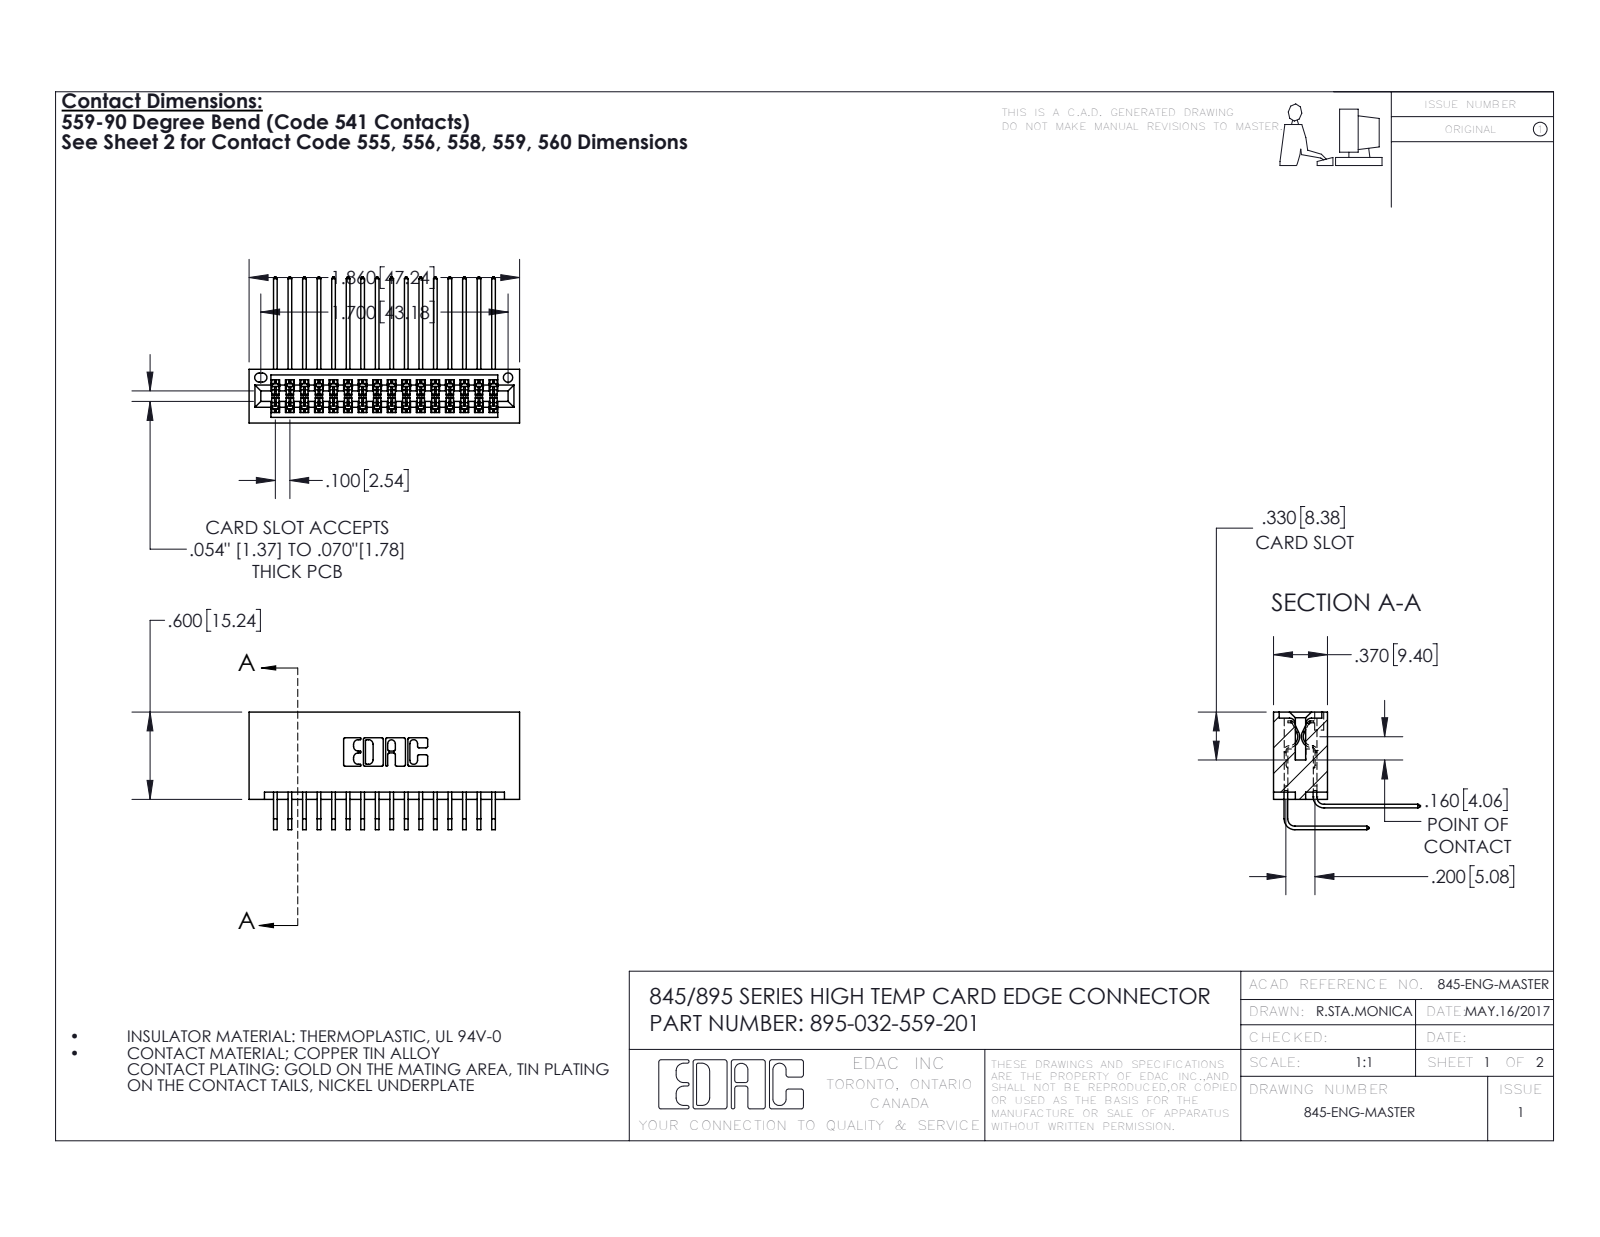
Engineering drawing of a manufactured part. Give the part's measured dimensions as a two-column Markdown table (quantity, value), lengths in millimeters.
| quantity | value |
| --- | --- |
| part name | 395-032-559-201; 345 Part_No Mounting Lugs; 345-292-001_559 Tail - 2; 345-292-001_558 559 Tail - 1 |
| STEP written by | SolidWorks 2016 (CONFIG_CONTROL_DESIGN) |
| units | millimeters |
| bodies | 33 solids, 1782 faces (1196 planar, 586 cylindrical, 0 other) |
| overall size | 47.2 × 25.5 × 20.5 |
| volume | 5 150 mm³ |
| surface area | 8 277 mm² |
| round holes (diameter × count) | 1.6 × 1 |
| partial cylindrical surfaces (radius × count) | 0.2 × 48, 0.3 × 22, 0.2 × 6, 0.8 × 6, 0.7 × 3, 0.4 × 2, 0.5 × 2, 0.6 × 2 |
| main face-to-face distances | 1.8, 7.6, 5.1, 9.4, 2.5, 6.9, 0.6, 5.7, 3.8, 4.4 |
